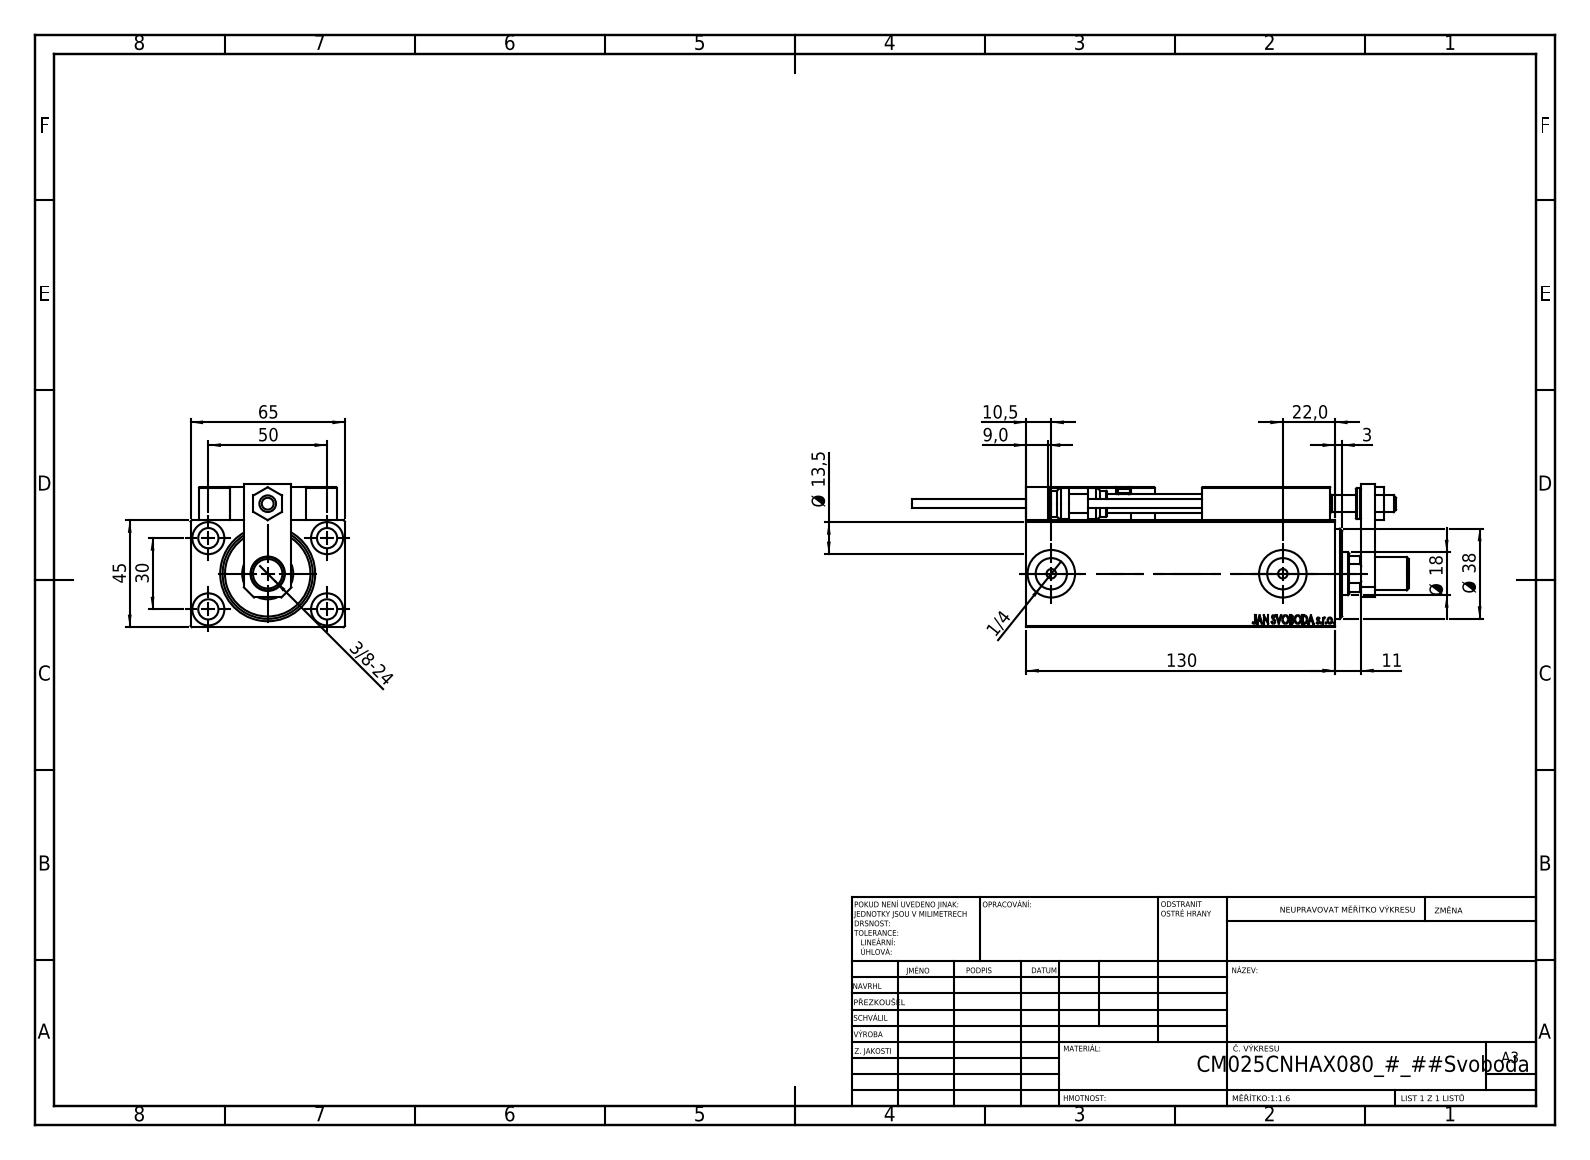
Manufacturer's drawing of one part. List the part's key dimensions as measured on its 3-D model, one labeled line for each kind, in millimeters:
Part name (STEP PRODUCT): ALLEN BOLT D8; V450CM_MALE_METRIC; V450CM_C_Body; TYC_L79 (+7 more)
STEP written by: SolidWorks 2019 (CONFIG_CONTROL_DESIGN)
Units: millimetres
Bodies: 24 solids, 1295 faces (563 planar, 192 cylindrical, 540 other)
Overall size (bounding box): 209 × 65 × 60.5
Volume: 376 763 mm³ · Surface area: 99 513 mm²
Round holes (diameter × count): ⌀4 ×6, ⌀8 ×5, ⌀8.5 ×5, ⌀3.2 ×4, ⌀13.5 ×4, ⌀5 ×2, ⌀13.16 ×2, ⌀20 ×2, ⌀7 ×1, ⌀14.5 ×1, ⌀18 ×1, ⌀21.5 ×1
Round bosses / shafts (diameter × count): ⌀5 ×2, ⌀3.8 ×2, ⌀14 ×1, ⌀13 ×1, ⌀12 ×1, ⌀11 ×1
Partial cylindrical surfaces — rounded edges, fillets, slot ends (radius × count): R0.3 ×30, R3 ×2, R8.5 ×1
Main face-to-face distances: 45, 65, 14, 6, 59, 3, 13, 3.5, 20, 141
Hole centre spacings: 29.15, 11.37, 20, 28.9, 29.59, 29.69, 30, 36.06
